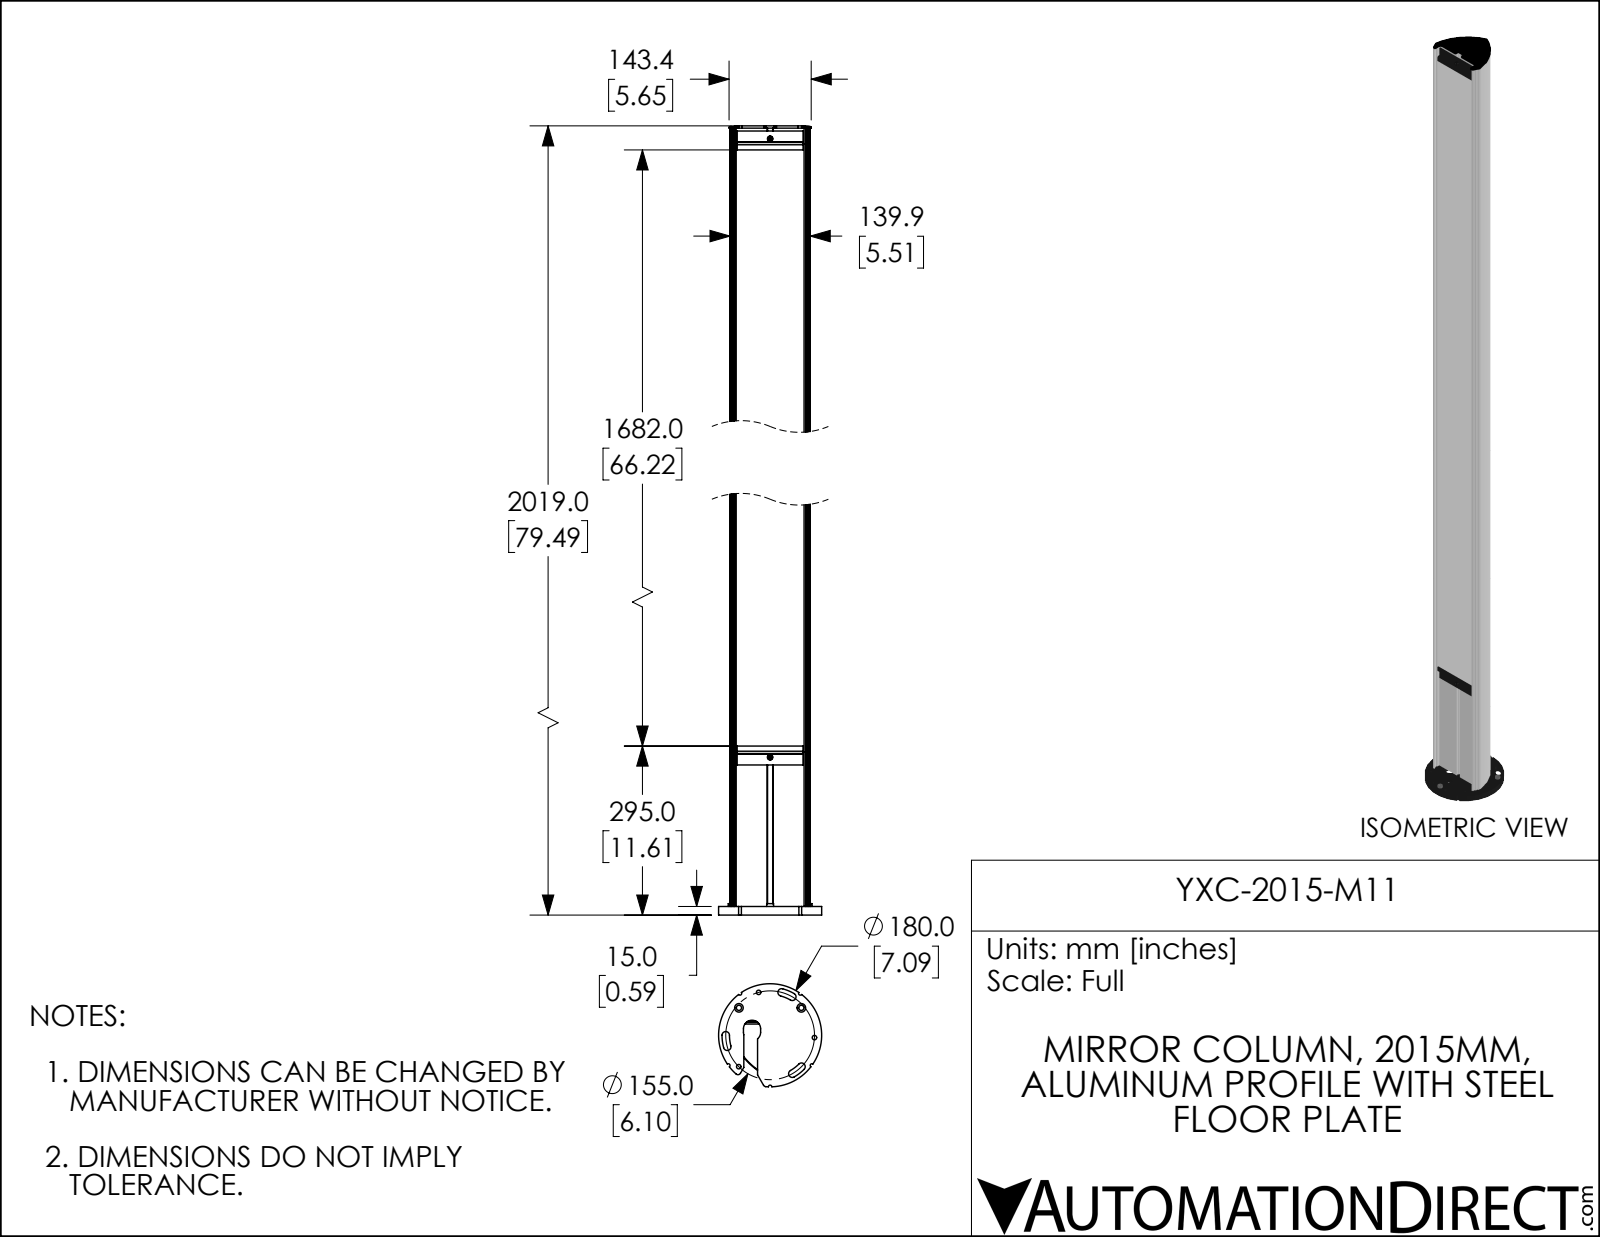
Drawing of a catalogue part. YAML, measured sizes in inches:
part_name: "YXC-2015-M11"
step_written_by: "SolidWorks 2019 (AUTOMOTIVE_DESIGN)"
units: inches
bodies: {solids: 1, faces: 290, planar: 187, cylindrical: 88, other: 15}
overall_size: [79.488, 7.087, 7.085]
volume: 1164
surface_area: 1630
round_holes:
  - {diameter: 0.307, count: 3}
  - {diameter: 0.591, count: 3}
  - {diameter: 0.354, count: 2}
  - {diameter: 0.173, count: 1}
round_bosses_or_shafts:
  - {diameter: 0.472, count: 3}
  - {diameter: 0.374, count: 2}
  - {diameter: 0.335, count: 2}
  - {diameter: 7.087, count: 1}
partial_cylinders:
  - {radius: 0.118, count: 9}
  - {radius: 0.256, count: 6}
  - {radius: 0.236, count: 5}
  - {radius: 0.039, count: 4}
  - {radius: 0.052, count: 4}
  - {radius: 4.685, count: 4}
  - {radius: 0.197, count: 3}
  - {radius: 0.052, count: 2}
face_to_face_distances: [0.157, 0.118, 0.335, 0.492, 0.453, 0.591, 0.098, 0.382, 0.224, 0.11]
hole_center_spacings: [2.146, 1.255, 1.257, 1.722, 2.235, 3.121, 3.717, 3.719]
